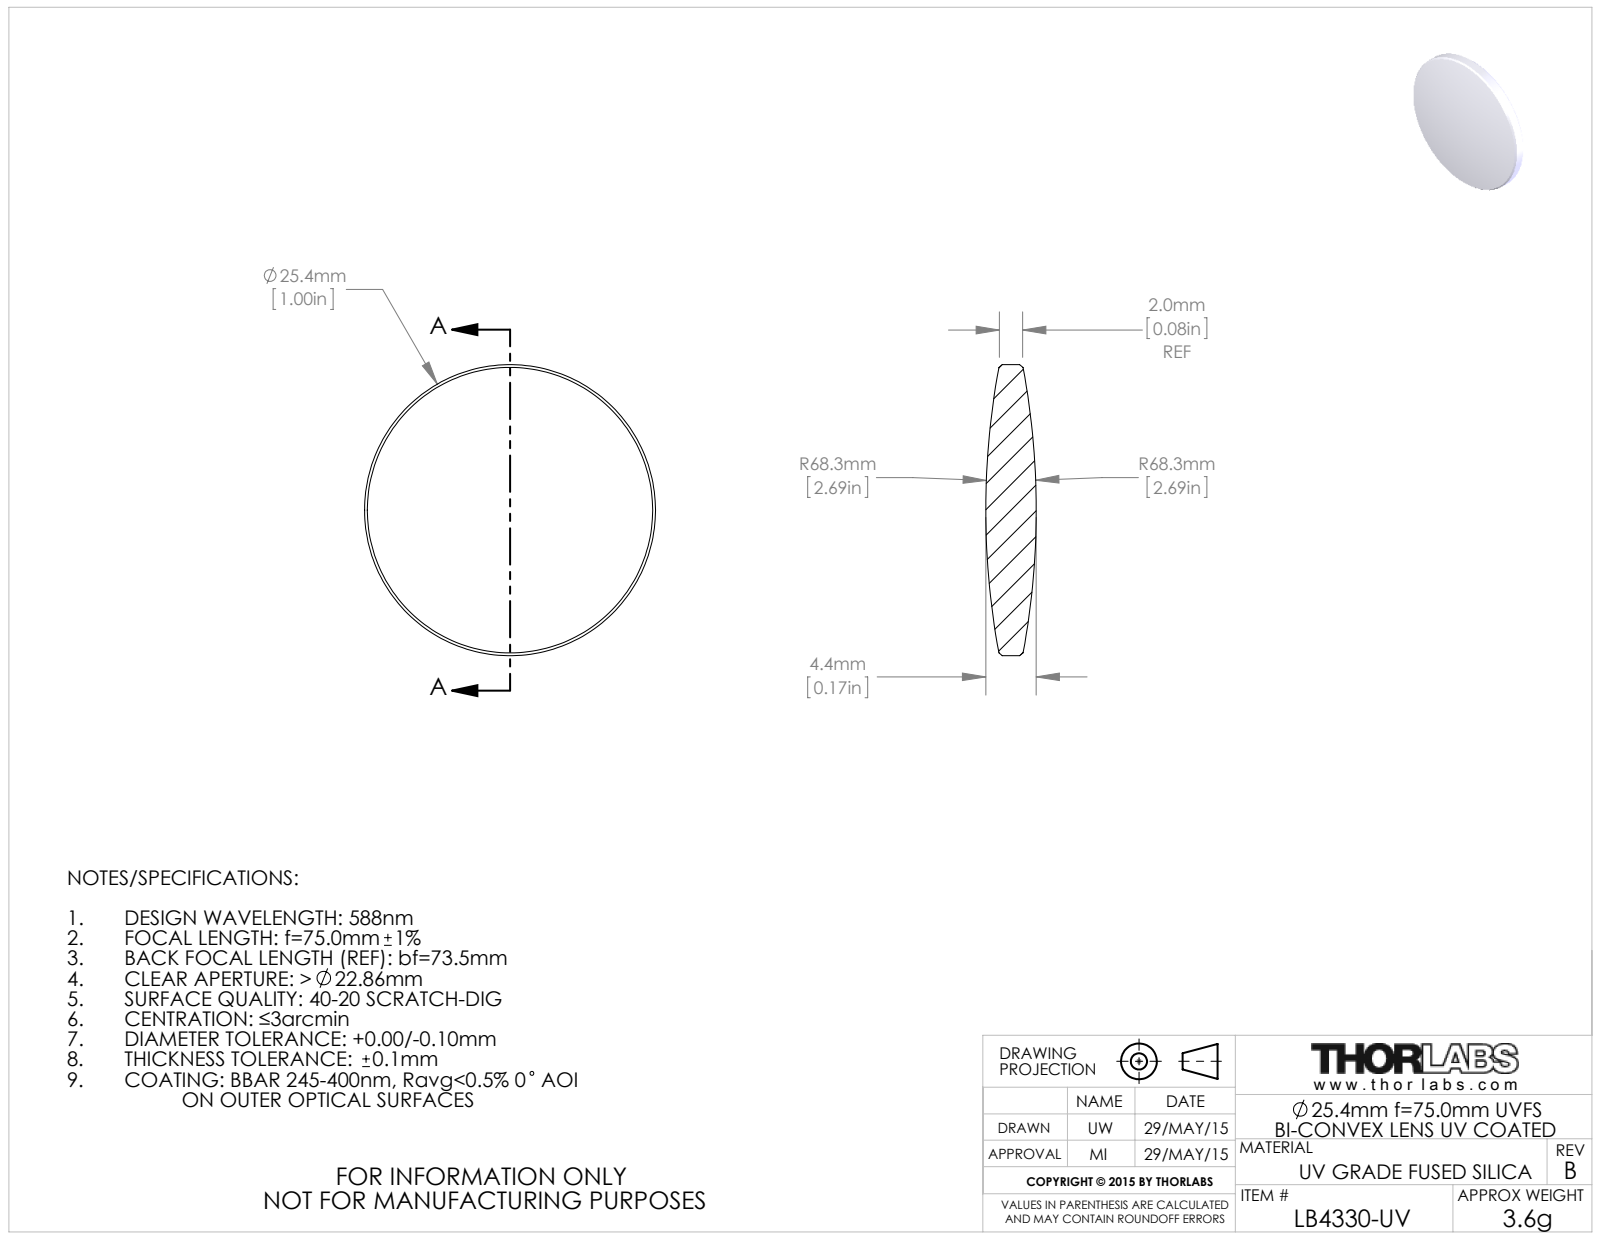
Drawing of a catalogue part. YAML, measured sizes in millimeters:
part_name: "4320-E0W"
step_written_by: "SolidWorks 2014 (CONFIG_CONTROL_DESIGN)"
units: millimeters
bodies: {solids: 1, faces: 10, planar: 0, cylindrical: 2, other: 8}
overall_size: [25.4, 25.4, 4.4]
volume: 1623
surface_area: 1165
round_bosses_or_shafts:
  - {diameter: 25.4, count: 1}
